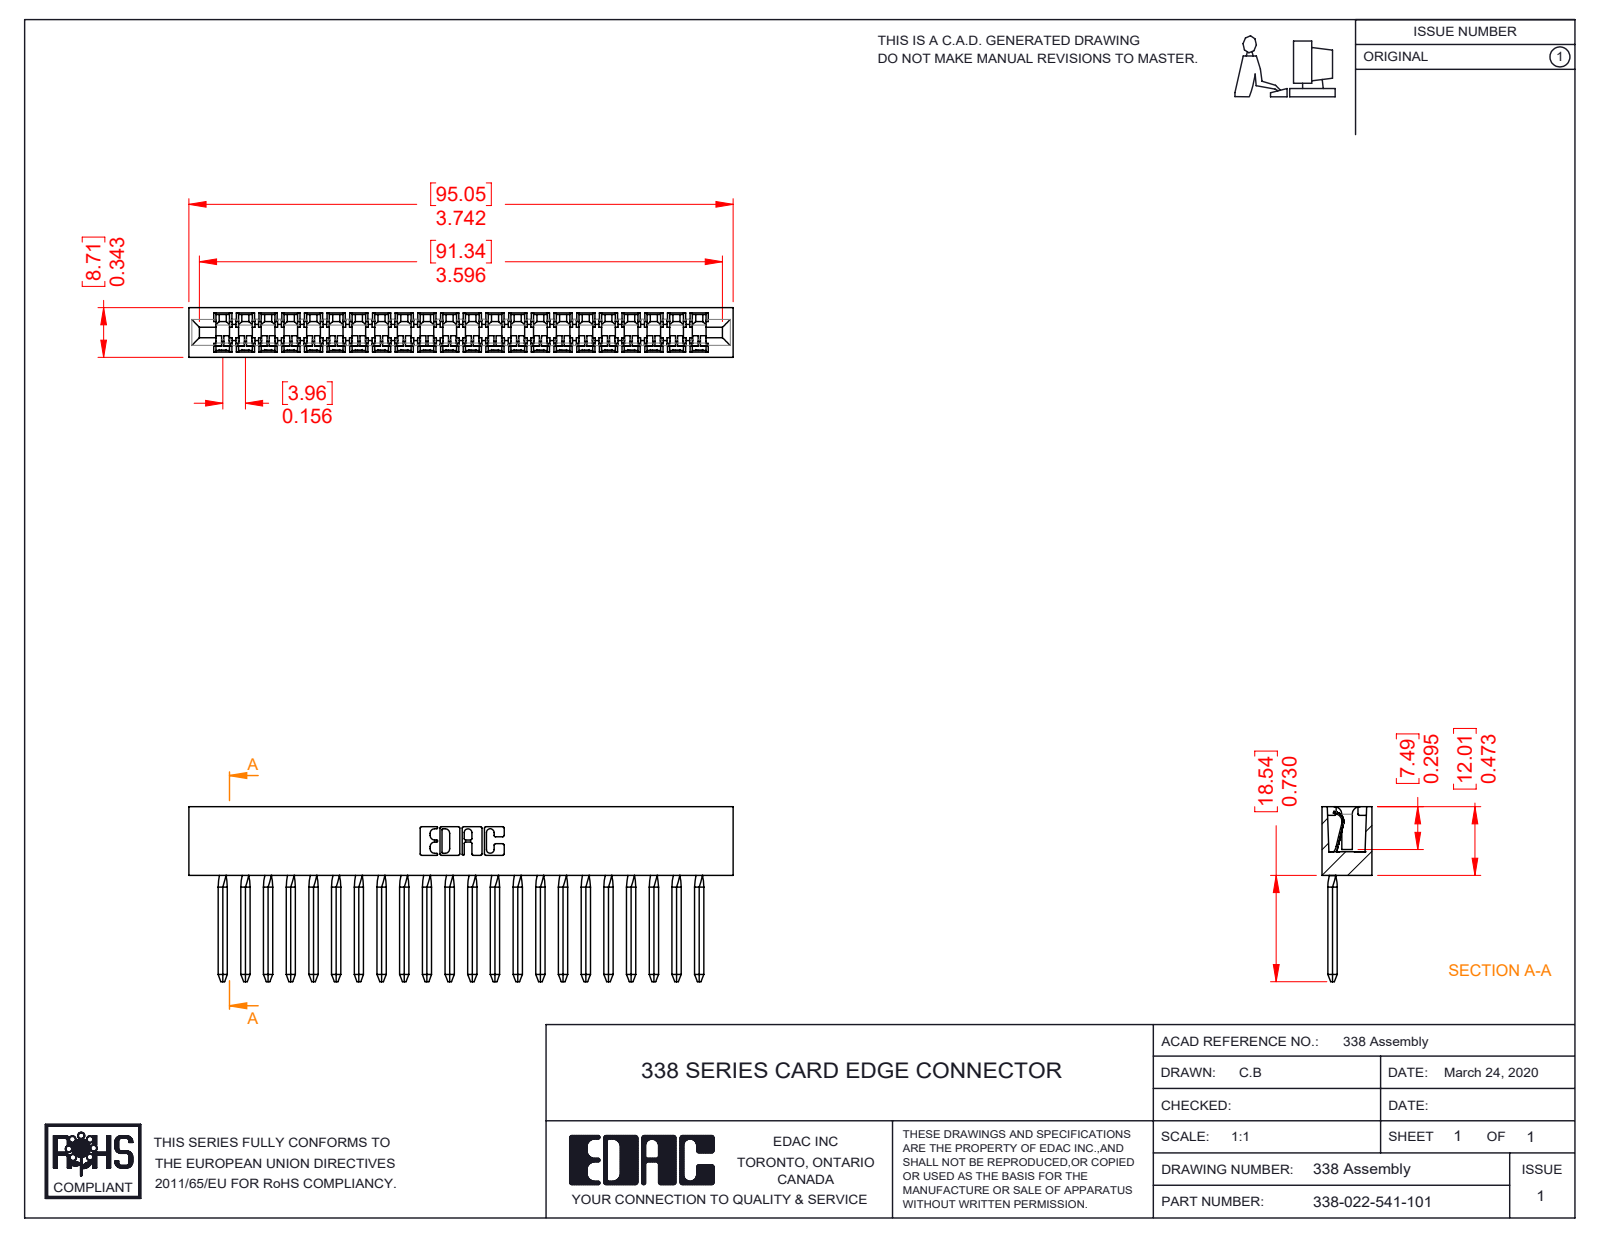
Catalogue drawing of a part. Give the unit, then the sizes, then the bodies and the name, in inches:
Units: inches
Overall size (bounding box): 3.742 × 1.203 × 0.343
Partial cylindrical surfaces — rounded edges, fillets, slot ends (radius × count): R0.025 ×90, R0.008 ×22, R0.01 ×22, R0.055 ×18, R0.067 ×18, R0.1 ×17, R0.007 ×6, R0.031 ×6
Main face-to-face distances: 0.343, 0.156, 0.624, 0.11, 0.78, 0.468, 0.207, 0.135, 1.248, 0.312
Volume: 0.424 in³ · Surface area: 17.9 in²
Bodies: 23 solids, 2132 faces (1476 planar, 568 cylindrical, 88 other)
Part name (STEP PRODUCT): 338-210-001_338-210-022-001; 338-022-541-101; 338-290-001_541
STEP written by: SolidWorks 2016 (CONFIG_CONTROL_DESIGN)
